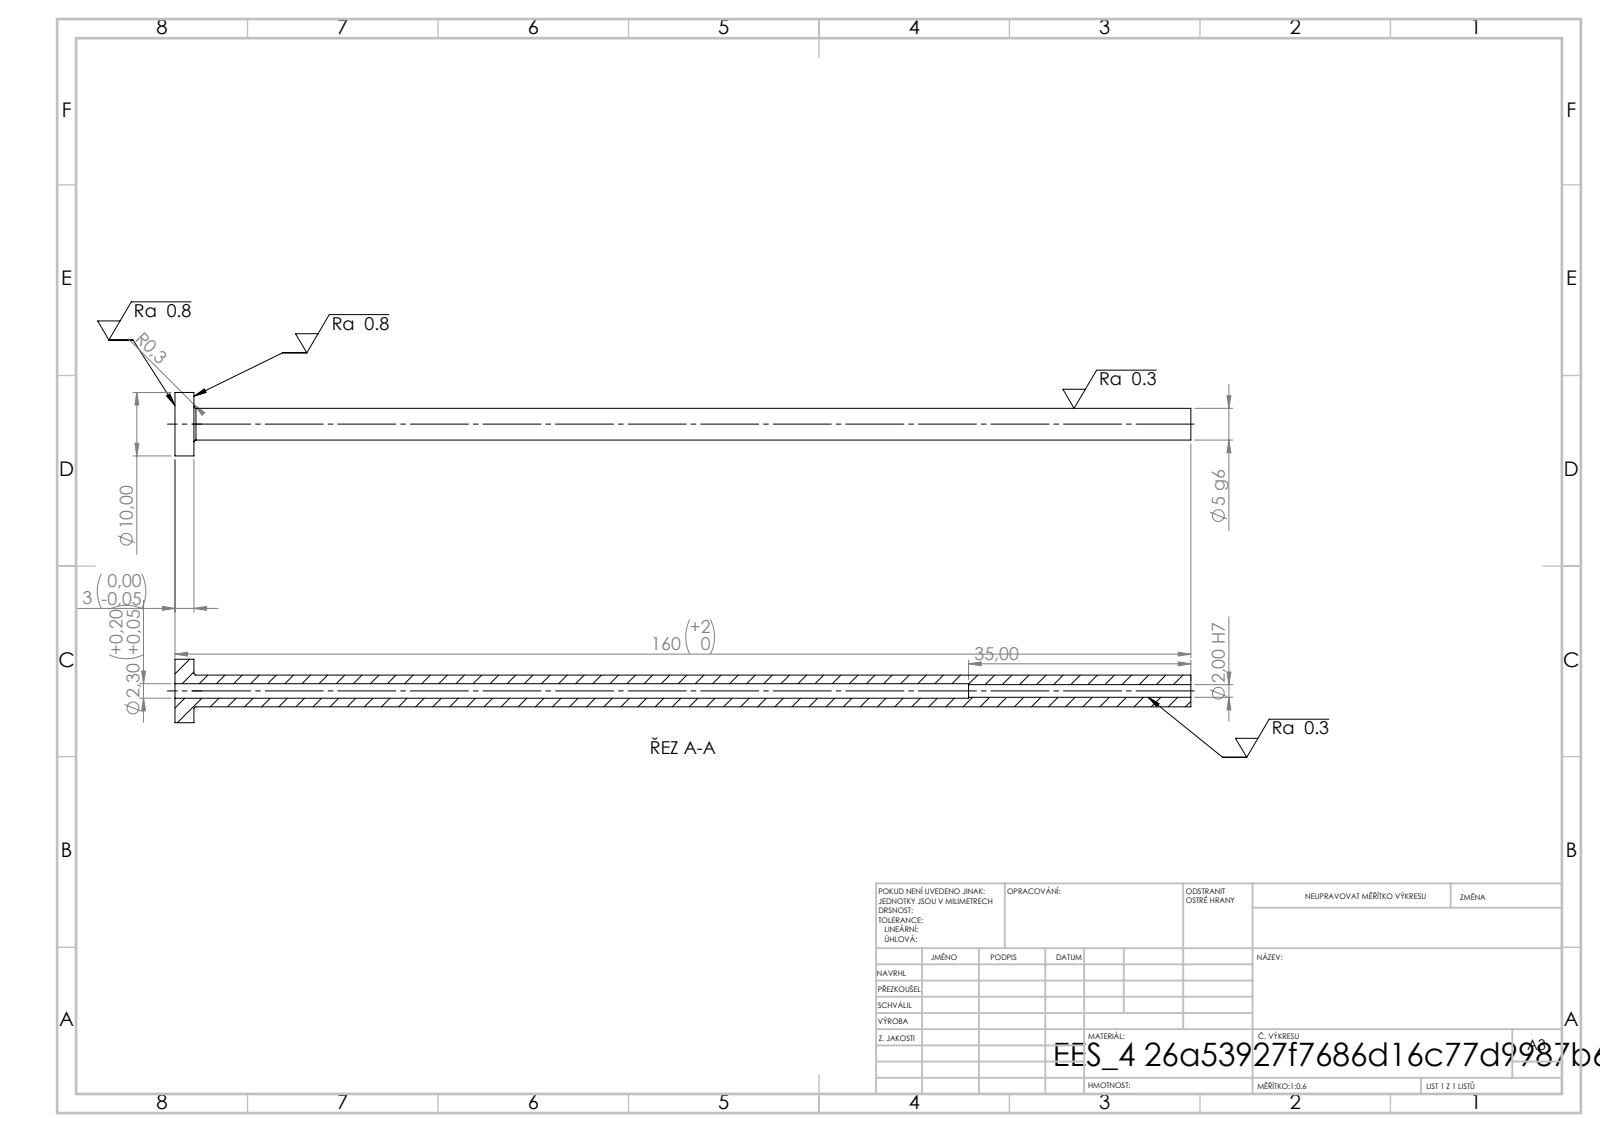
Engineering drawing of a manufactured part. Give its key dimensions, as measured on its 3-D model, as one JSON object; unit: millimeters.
{"step_written_by": "SolidWorks 2019 (CONFIG_CONTROL_DESIGN)", "units": "millimeters", "bodies": {"solids": 1, "faces": 14, "planar": 4, "cylindrical": 8, "other": 2}, "overall_size": [160, 10, 10], "volume_mm3": 2689, "surface_area_mm2": 3832, "round_holes": [[2, 1], [2.3, 1]], "round_bosses_or_shafts": [[10, 1], [5, 1]], "face_to_face_distances": [3, 160, 157, 125, 122, 35]}
